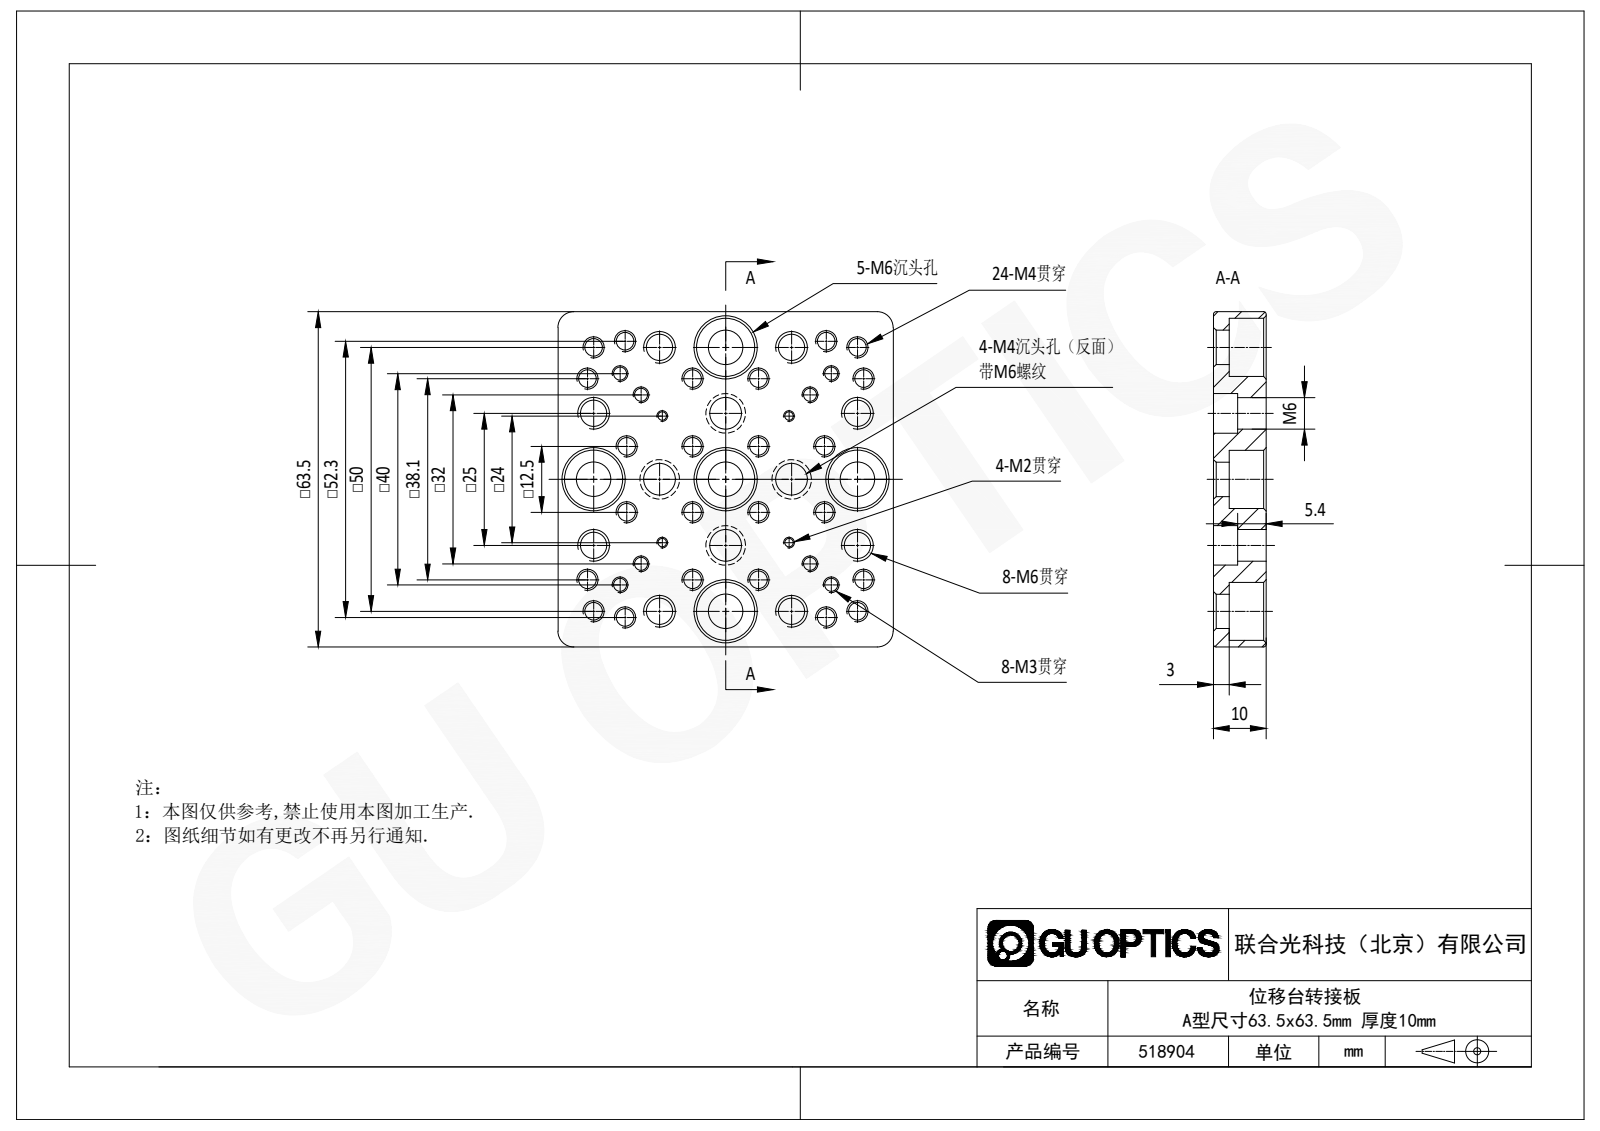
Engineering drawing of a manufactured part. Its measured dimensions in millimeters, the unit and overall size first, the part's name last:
Units: millimetres
Overall size (bounding box): 63.5 × 63.5 × 10
Round holes (diameter × count): ⌀3.3 ×24, ⌀2.5 ×8, ⌀5 ×8, ⌀6.5 ×5, ⌀11 ×5, ⌀1.6 ×4, ⌀6 ×4, ⌀7.5 ×4
Partial cylindrical surfaces — rounded edges, fillets, slot ends (radius × count): R0.5 ×8, R3 ×4
Main face-to-face distances: 10, 63.5, 3, 7, 4.6, 1.6, 5.4
Hole centre spacings: 12.5, 19.76, 27.95, 25, 8.84, 31.87, 19.75, 20.05
Volume: 30 798 mm³ · Surface area: 15 809 mm²
Bodies: 1 solid, 151 faces (15 planar, 74 cylindrical, 62 other)
STEP written by: SolidWorks 2020 (CONFIG_CONTROL_DESIGN)
